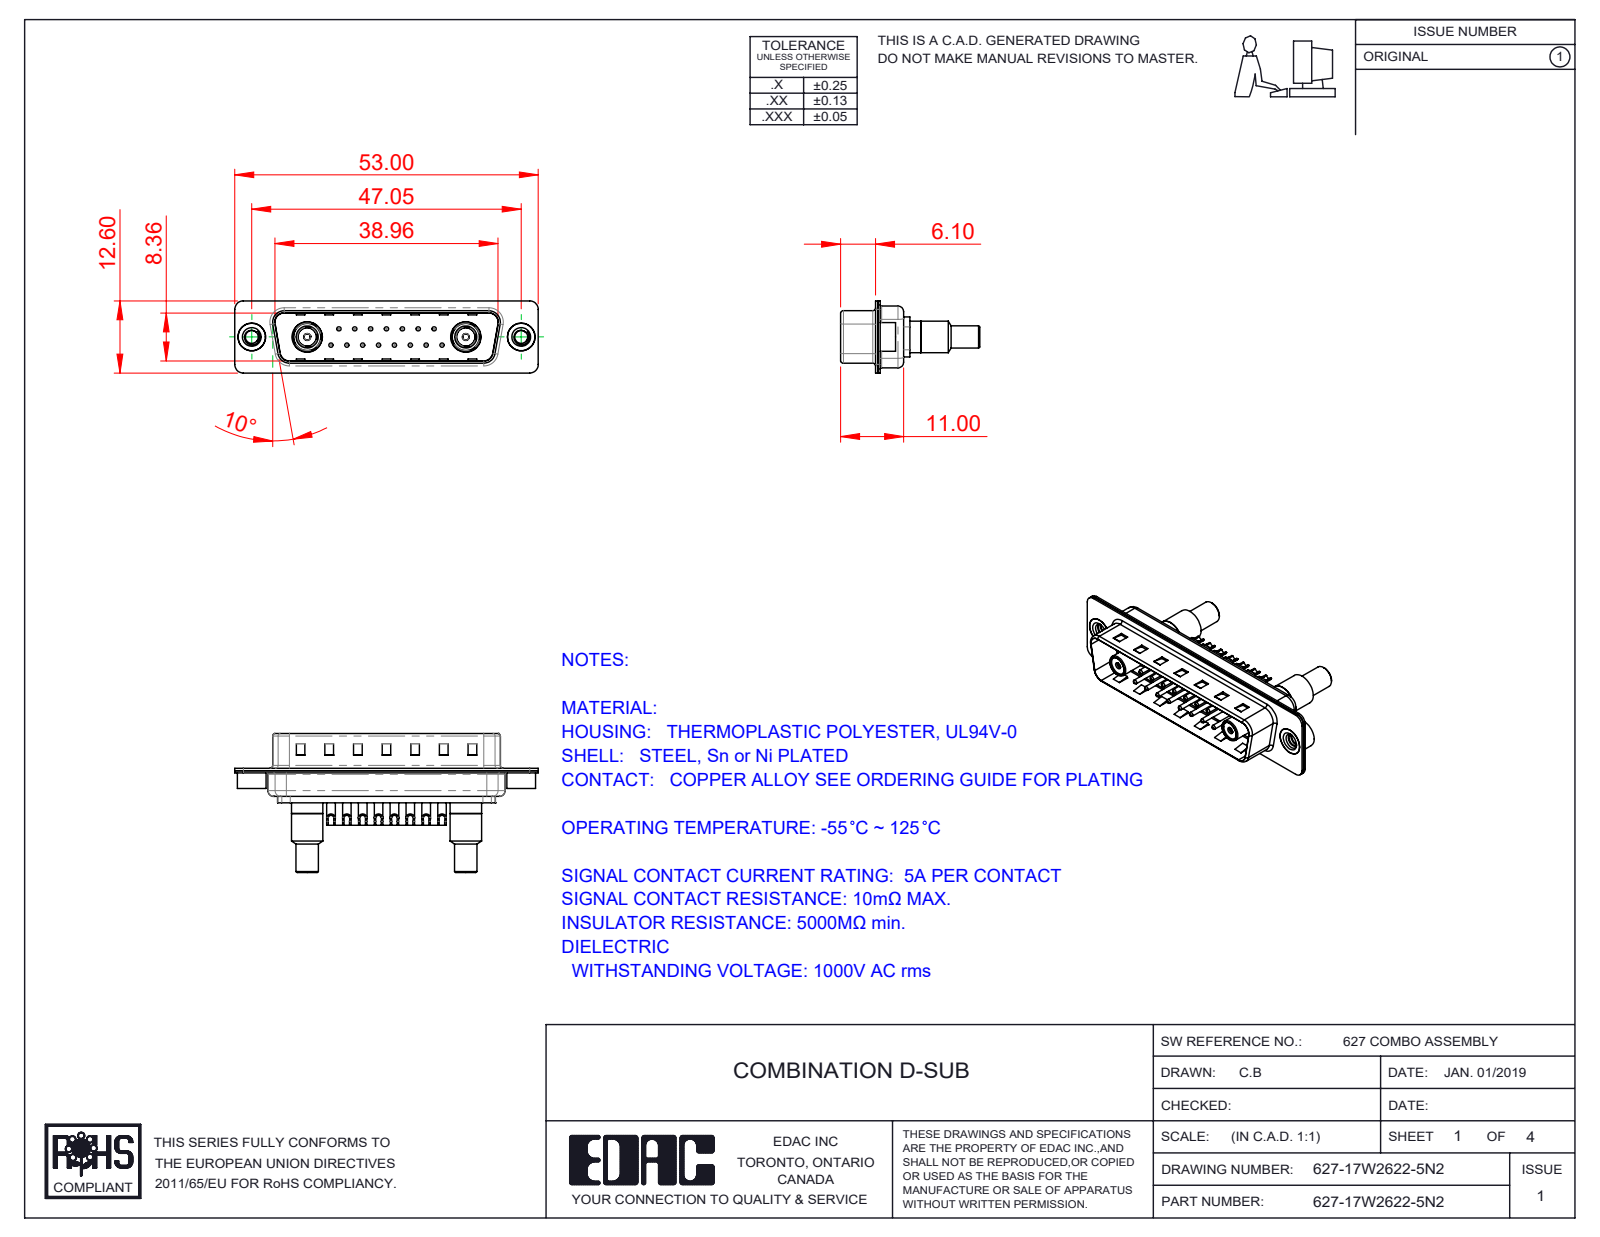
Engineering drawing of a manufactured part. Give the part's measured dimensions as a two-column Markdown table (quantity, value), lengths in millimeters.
| quantity | value |
| --- | --- |
| part name | Socket_Solder Cup; Insulator Socket 2; Insulator Socket; Co-Ax Jack_Solder Cup Tail (+8 more) |
| STEP written by | SolidWorks 2016 (CONFIG_CONTROL_DESIGN) |
| units | millimeters |
| bodies | 32 solids, 1191 faces (386 planar, 505 cylindrical, 300 other) |
| overall size | 53 × 24.3 × 12.6 |
| volume | 2 996 mm³ |
| surface area | 8 580 mm² |
| round holes (diameter × count) | 1.6 × 17, 0.75 × 15, 1 × 15, 2 × 15, 4.8 × 4, 0.8 × 2, 1.1 × 2, 1.2 × 2, 1.5 × 2, 1.8 × 2, 2.26 × 2, 2.5 × 2 |
| round bosses / shafts (diameter × count) | 1.5 × 15, 5.5 × 2, 5.2 × 2, 5 × 2, 4.9 × 2, 4.75 × 2, 4.73 × 2, 3.9 × 2 |
| partial cylindrical surfaces (radius × count) | 1.5 × 17, 2 × 12, 0.5 × 8, 1.6 × 8, 1 × 6, 0.25 × 4, 0.6 × 4, 0.65 × 4 |
| main face-to-face distances | 0.4, 0.82, 9.58, 8.76, 6, 1.5, 0.8, 1.9, 1.22, 9.98 |
| hole center spacings | 3.16, 2.77, 5.54, 8.31, 5.04, 7.49, 11.08, 5.03 |
